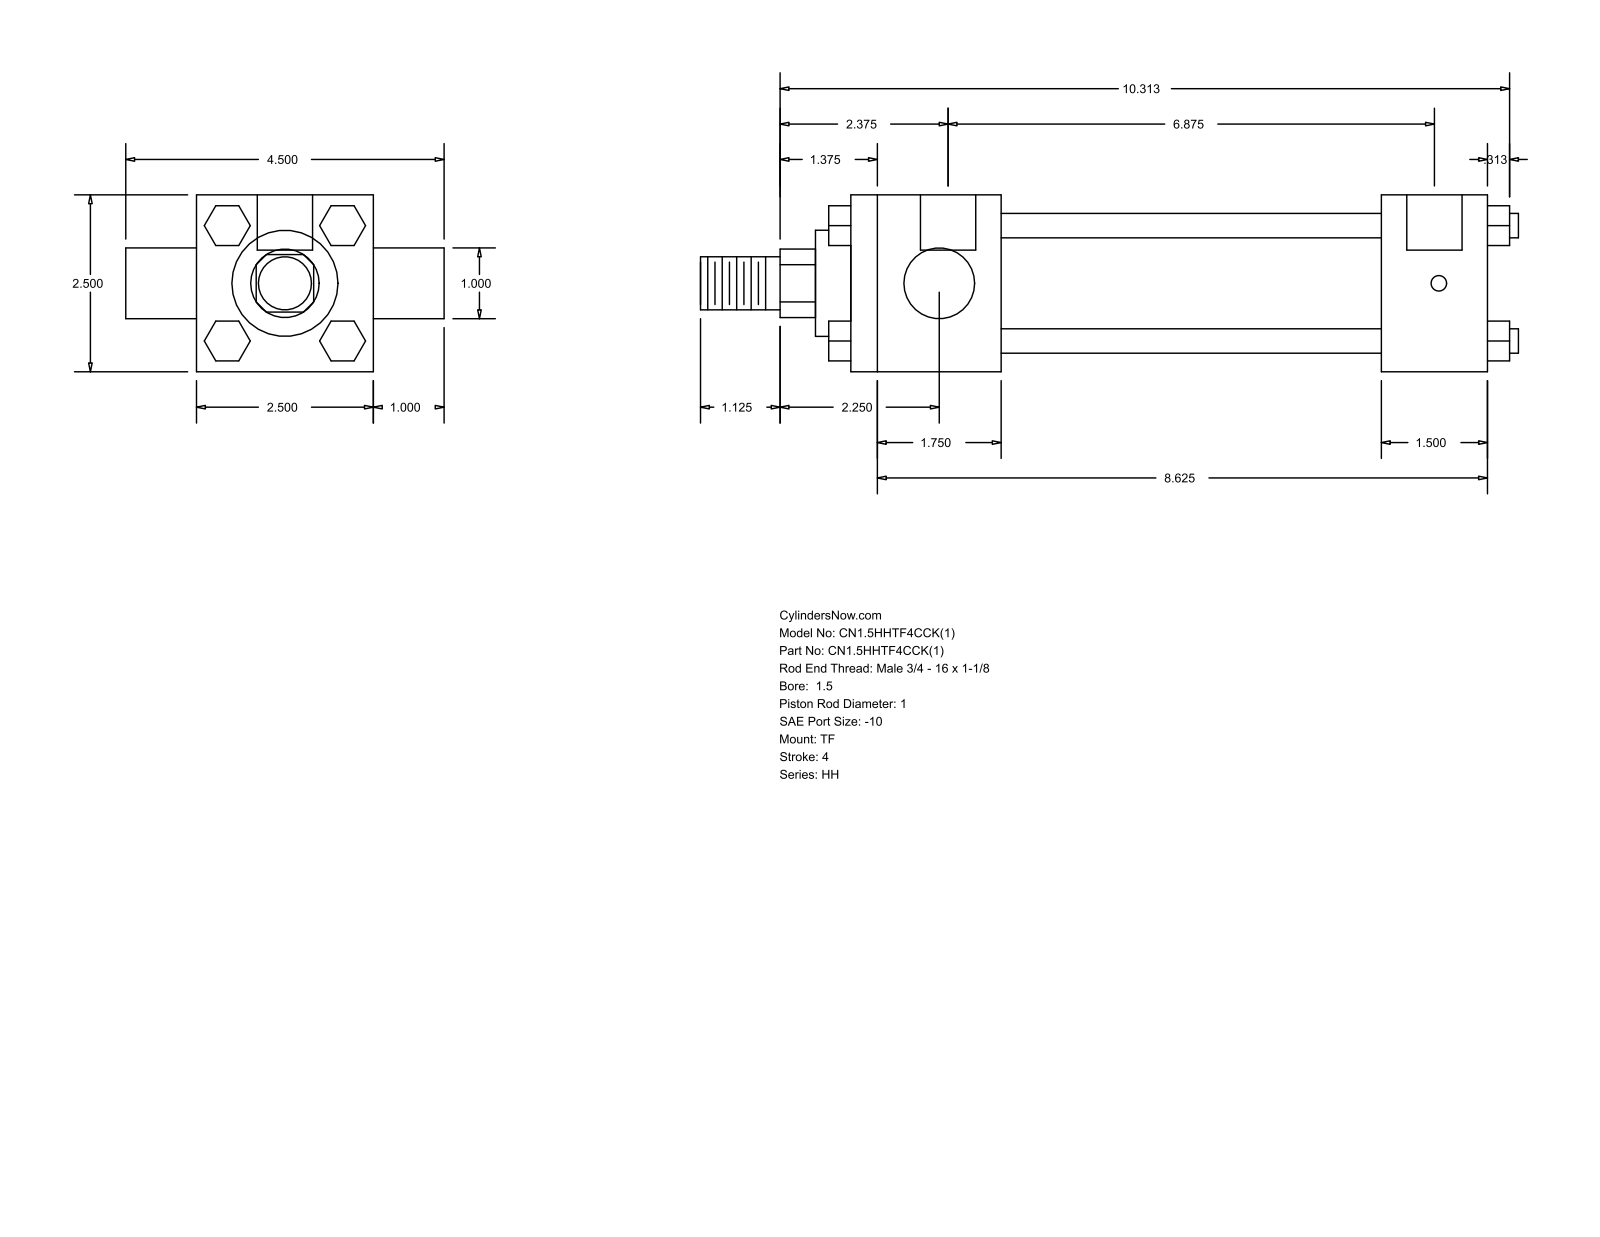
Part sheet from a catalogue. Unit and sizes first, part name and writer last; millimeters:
Units: millimetres
Overall size (bounding box): 293.69 × 114.3 × 63.5
Round holes (diameter × count): ⌀5.56 ×3, ⌀19.84 ×2
Round bosses / shafts (diameter × count): ⌀8.76 ×4, ⌀25.4 ×2, ⌀44.45 ×1, ⌀38.1 ×1, ⌀19.05 ×1
Partial cylindrical surfaces — rounded edges, fillets, slot ends (radius × count): R12.29 ×1
Main face-to-face distances: 63.5, 38.1, 174.62, 136.52, 53.98, 190.5, 228.6, 25.4, 20.7, 14.29
Hole centre spacings: 1.59, 176.21, 174.62, 177.8
Bodies: 0 solids, 120 faces (92 planar, 28 cylindrical, 0 other)
Part name (STEP PRODUCT): HH_TF__0150_1
STEP written by: GSSL Pune (CONFIG_CONTROL_DESIGN)
